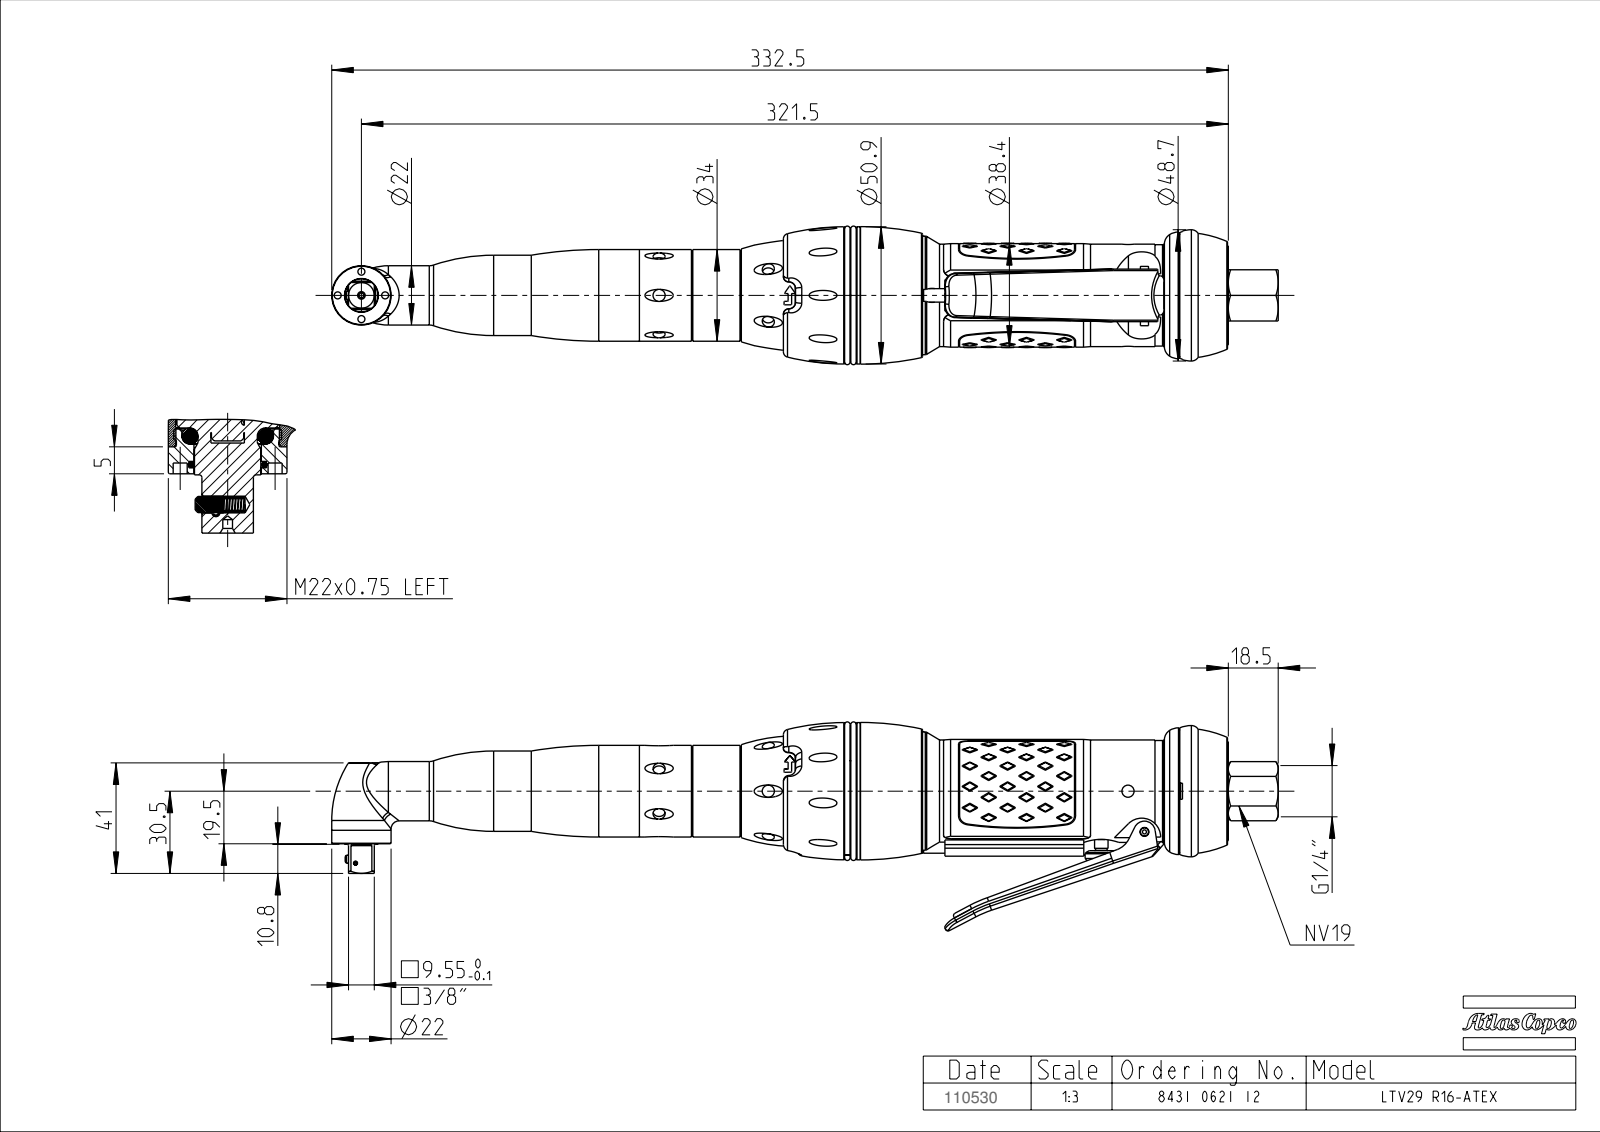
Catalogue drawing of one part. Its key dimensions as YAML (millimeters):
part_name: "TMP93732_SW"
step_written_by: "PRO/ENGINEER BY PARAMETRIC TECHNOLOGY CORPORATION, 2008310 (CONFIG_CONTROL_DESIGN)"
units: millimeters
bodies: {solids: 0, faces: 380, planar: 49, cylindrical: 144, other: 187}
overall_size: [351, 77.55, 51.4]
round_holes:
  - {diameter: 4.5, count: 4}
  - {diameter: 8, count: 1}
  - {diameter: 8.09, count: 1}
  - {diameter: 11, count: 1}
  - {diameter: 11.5, count: 1}
  - {diameter: 11.7, count: 1}
  - {diameter: 15, count: 1}
round_bosses_or_shafts:
  - {diameter: 22, count: 2}
  - {diameter: 50.9, count: 1}
  - {diameter: 44, count: 1}
  - {diameter: 38.4, count: 1}
  - {diameter: 38, count: 1}
  - {diameter: 37.6, count: 1}
  - {diameter: 35.8, count: 1}
  - {diameter: 34, count: 1}
partial_cylinders:
  - {radius: 1, count: 6}
  - {radius: 2.5, count: 2}
  - {radius: 4, count: 2}
  - {radius: 5, count: 2}
  - {radius: 19, count: 2}
  - {radius: 20.5, count: 2}
  - {radius: 1.5, count: 1}
  - {radius: 6, count: 1}
face_to_face_distances: [19, 3, 19.25, 1.5, 1.75, 17.75, 17.5, 4.97, 14.53, 4.72]
